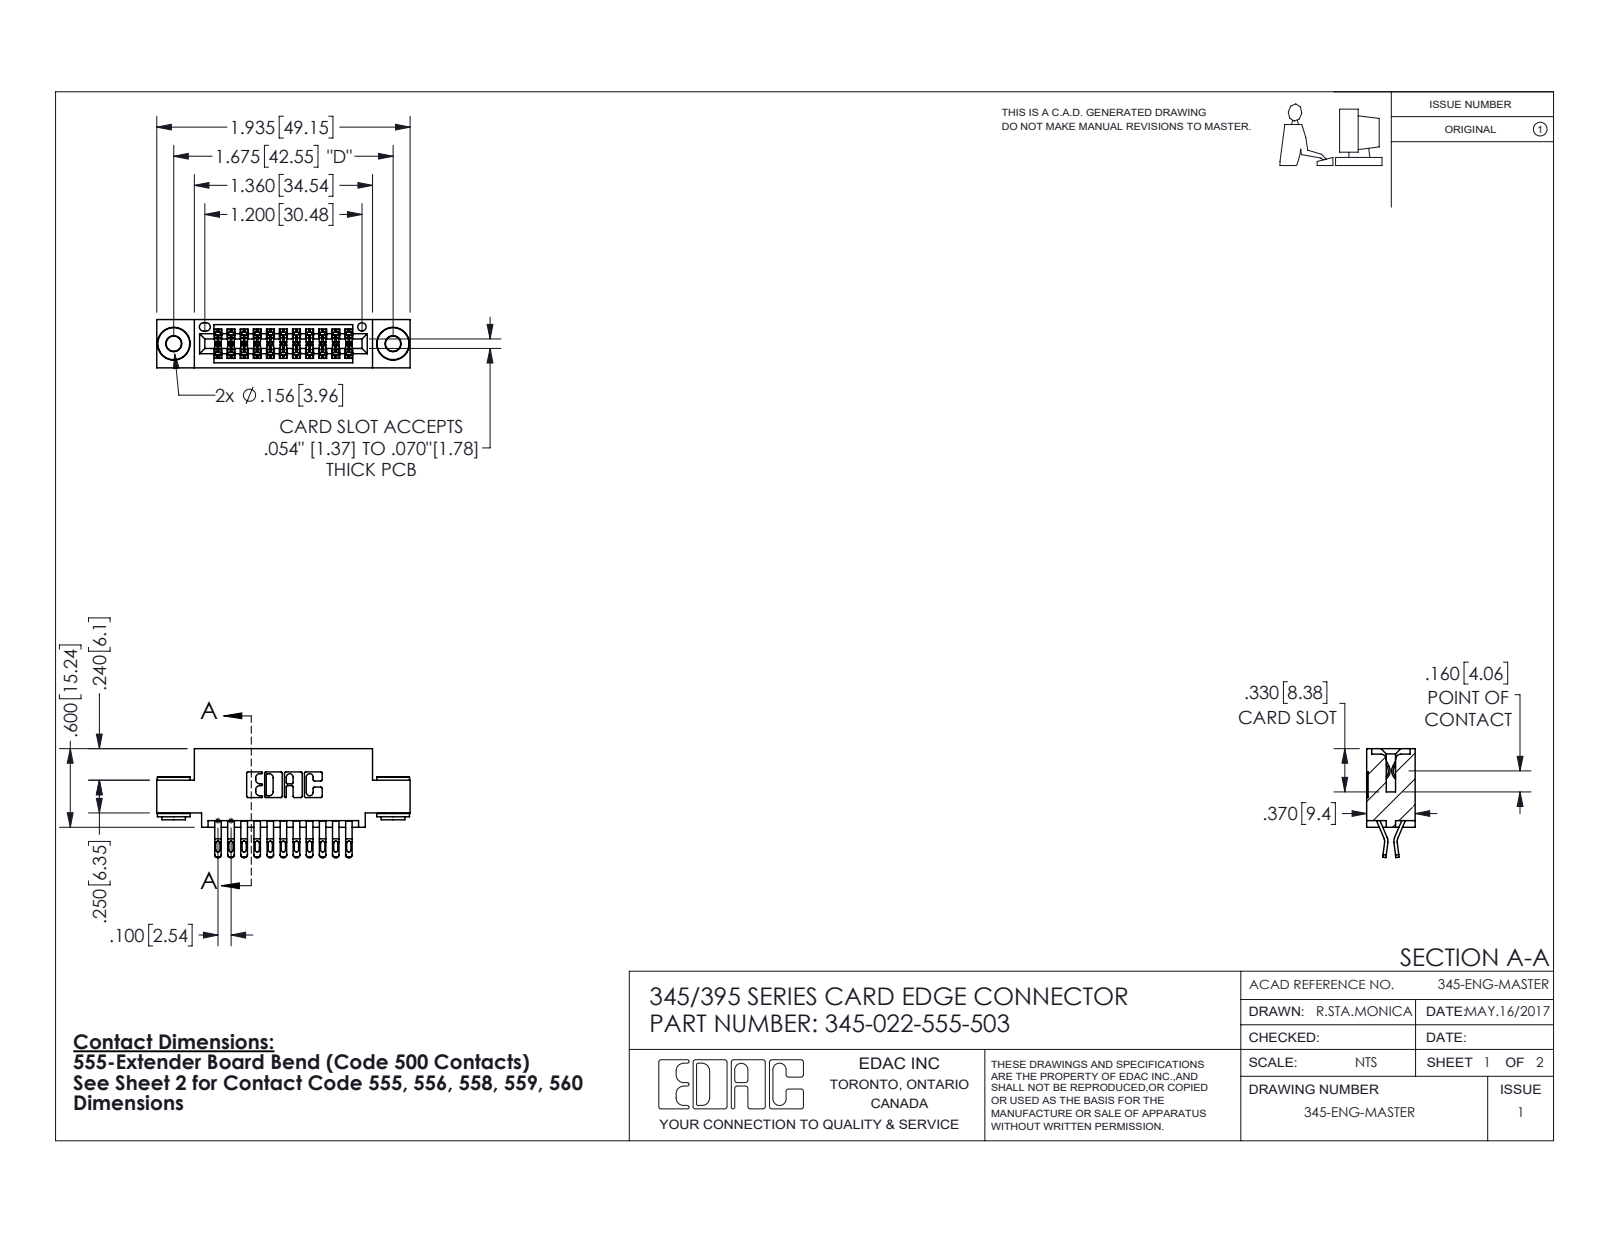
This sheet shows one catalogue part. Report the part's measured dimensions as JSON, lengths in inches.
{"part_name": "345-022-555-503; 345 Part_0.110 Offset - 0.156 Dia-TH; 345-292-001_555 Tail; 345-250-002_345-250-002-102", "step_written_by": "SolidWorks 2016 (CONFIG_CONTROL_DESIGN)", "units": "inches", "bodies": {"solids": 25, "faces": 1400, "planar": 776, "cylindrical": 616, "other": 8}, "overall_size": [1.935, 0.832, 0.37], "volume_in3": 0.274, "surface_area_in2": 10.18, "round_holes": [[0.116, 2], [0.156, 2], [0.064, 1]], "round_bosses_or_shafts": [[0.25, 2], [0.18, 2], [0.136, 2]], "partial_cylinders_radius": [[0.016, 55], [0.02, 44], [0.006, 33], [0.01, 22], [0.007, 6], [0.031, 6], [0.026, 3], [0.01, 2]], "face_to_face_distances": [0.072, 0.298, 0.2, 0.37, 0.025, 0.098, 0.272, 0.225, 0.1, 0.6], "hole_center_spacings": [0.27, 1.443, 1.675]}
